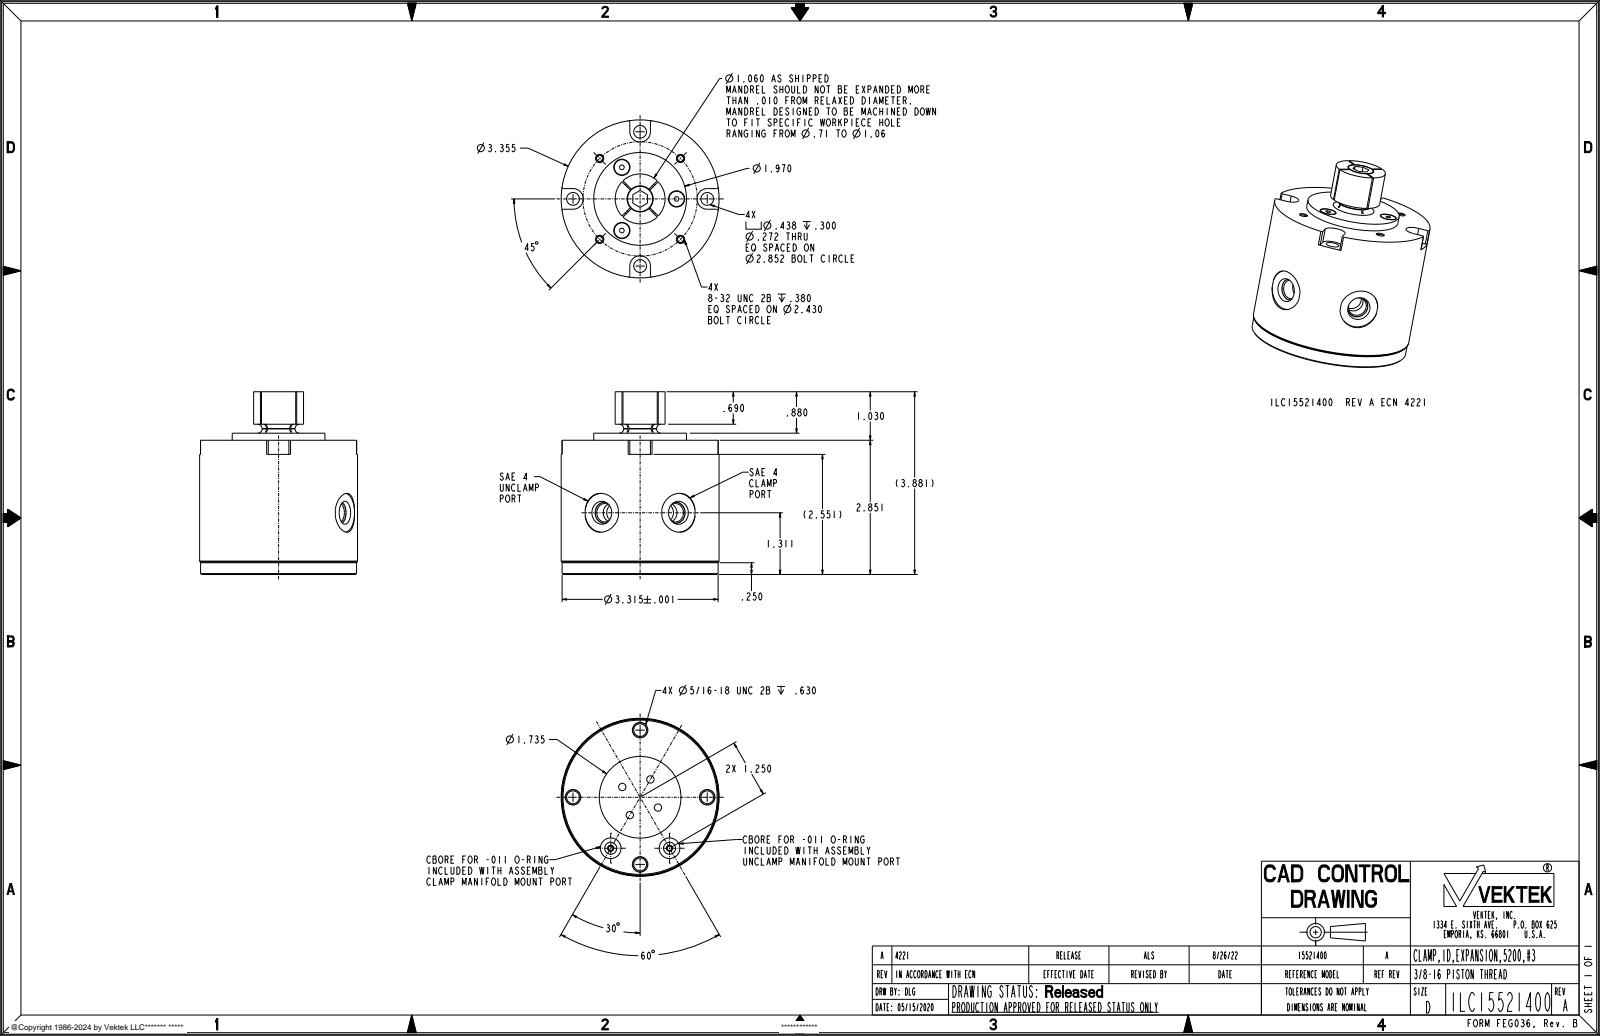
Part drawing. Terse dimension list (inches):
name: ILC15521400
written by: CREO PARAMETRIC BY PTC INC, 2021164 (AUTOMOTIVE_DESIGN)
unit: in
bodies: 1 solid, 268 faces (96 planar, 118 cylindrical, 54 other)
size: 3.881 × 3.355 × 3.355
volume: 25.11 in³; area: 71.08 in²
holes: 4× ⌀0.135, 4× ⌀0.156, 4× ⌀0.272, 3× ⌀0.345, 2× ⌀0.1, 2× ⌀0.256, 2× ⌀0.392, 2× ⌀0.438, 2× ⌀0.825, 1× ⌀0.555, 1× ⌀1.735
bosses: 4× ⌀0.313, 4× ⌀0.165, 3× ⌀0.325, 2× ⌀0.437, 2× ⌀0.118, 1× ⌀3.355, 1× ⌀3.315, 1× ⌀1.97
rounds: 8× R0.03, 4× R0.219
face distances: 2.851, 0.15, 3.001, 2.986, 2.836, 0.015, 0.03, 0.88, 1.03, 3.866
hole spacings: 1.029, 2.441, 1.688, 0.437, 0.619, 0.8, 1.07, 1.18
